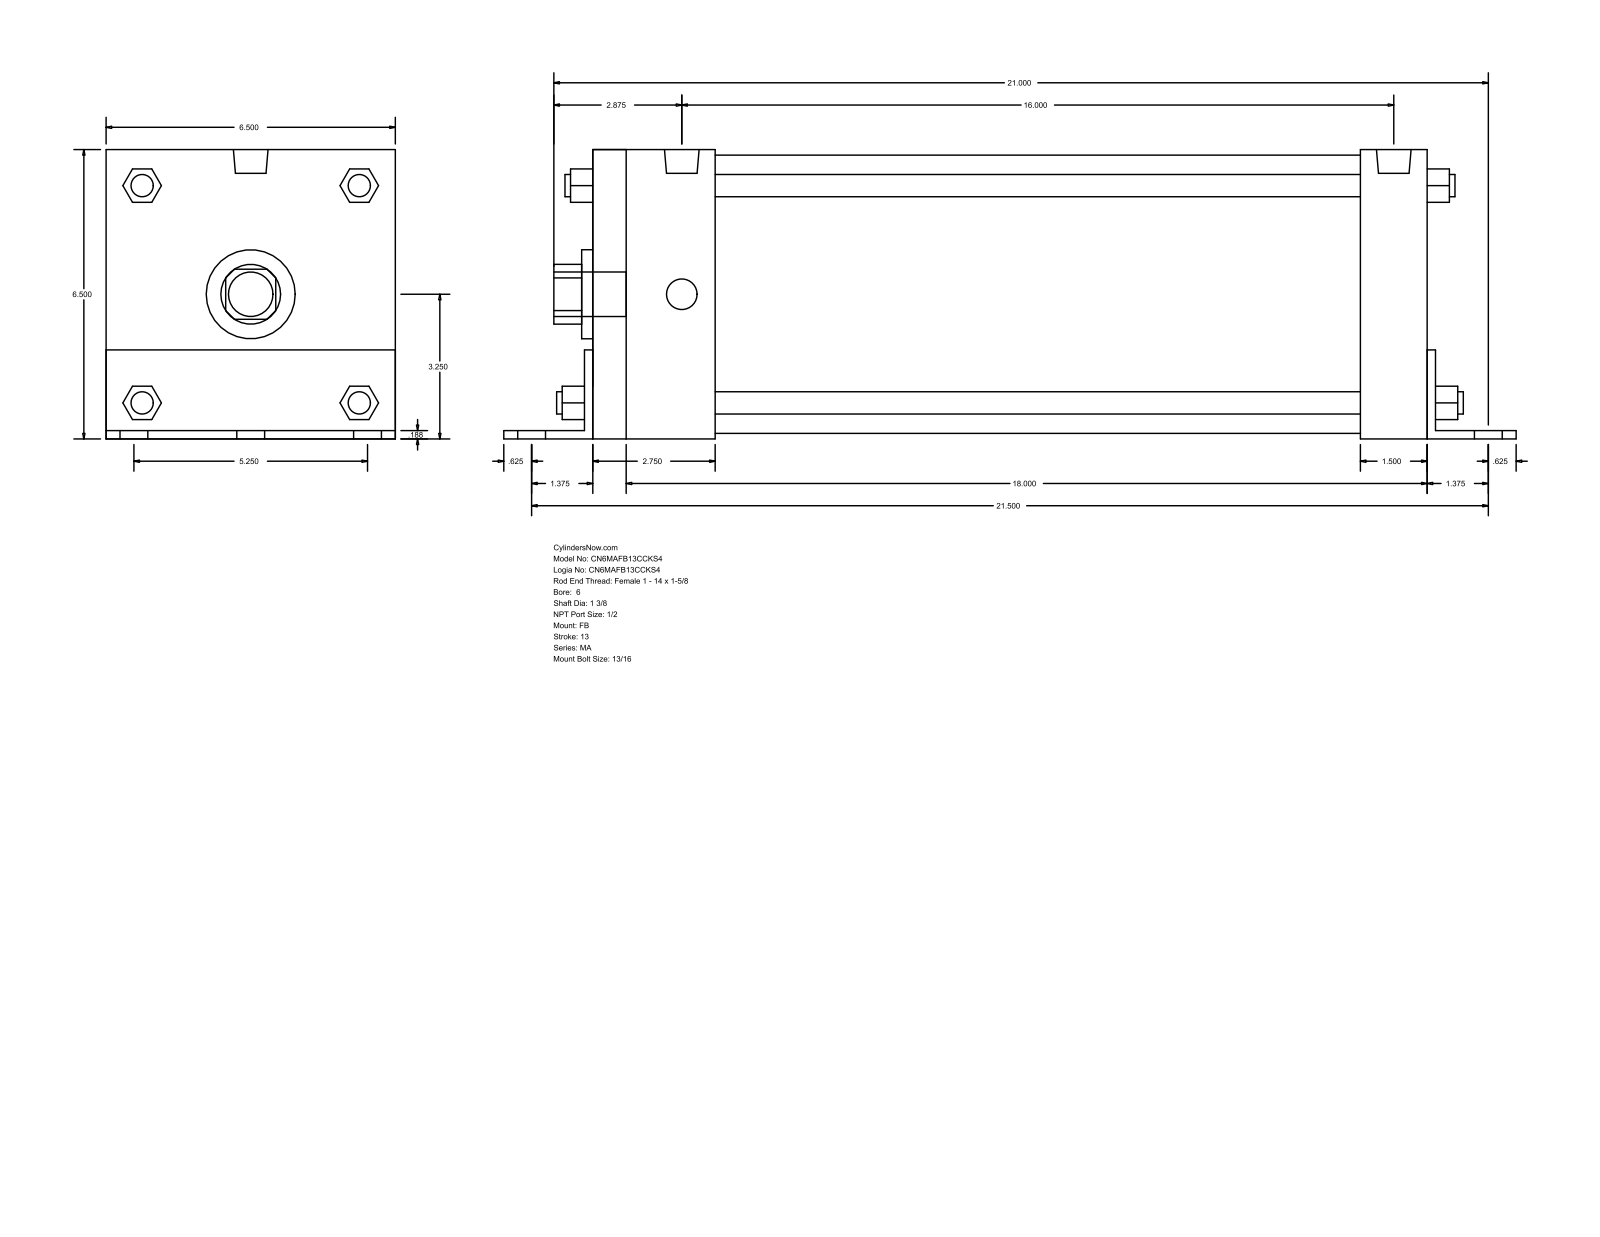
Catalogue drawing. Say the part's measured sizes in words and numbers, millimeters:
The part is named "MA_FB__0600_1.375". Its 3-D file was written by "GSSL Pune (CONFIG_CONTROL_DESIGN)". It is 0 solids with 140 faces: 105 planar, 35 cylindrical and 0 other. Overall it measures 574.67 by 165.15 by 165.1 millimeters. Round holes: 1 of diameter 34.92, 1 of diameter 50.8, 1 of diameter 158.75. Round bosses or shafts: 6 of diameter 20.64, 4 of diameter 17.46, 4 of diameter 12.7, 2 of diameter 19.77, 1 of diameter 25.4. Partial cylindrical surfaces (rounded edges, fillets, slot ends): 1 of radius 17.06, 1 of radius 32.05. The main face-to-face distances are 165.1, 4.76, 473.07, 165.15, 4.71, 160.39, 4.77, 38.1, 477.84, 482.6.
